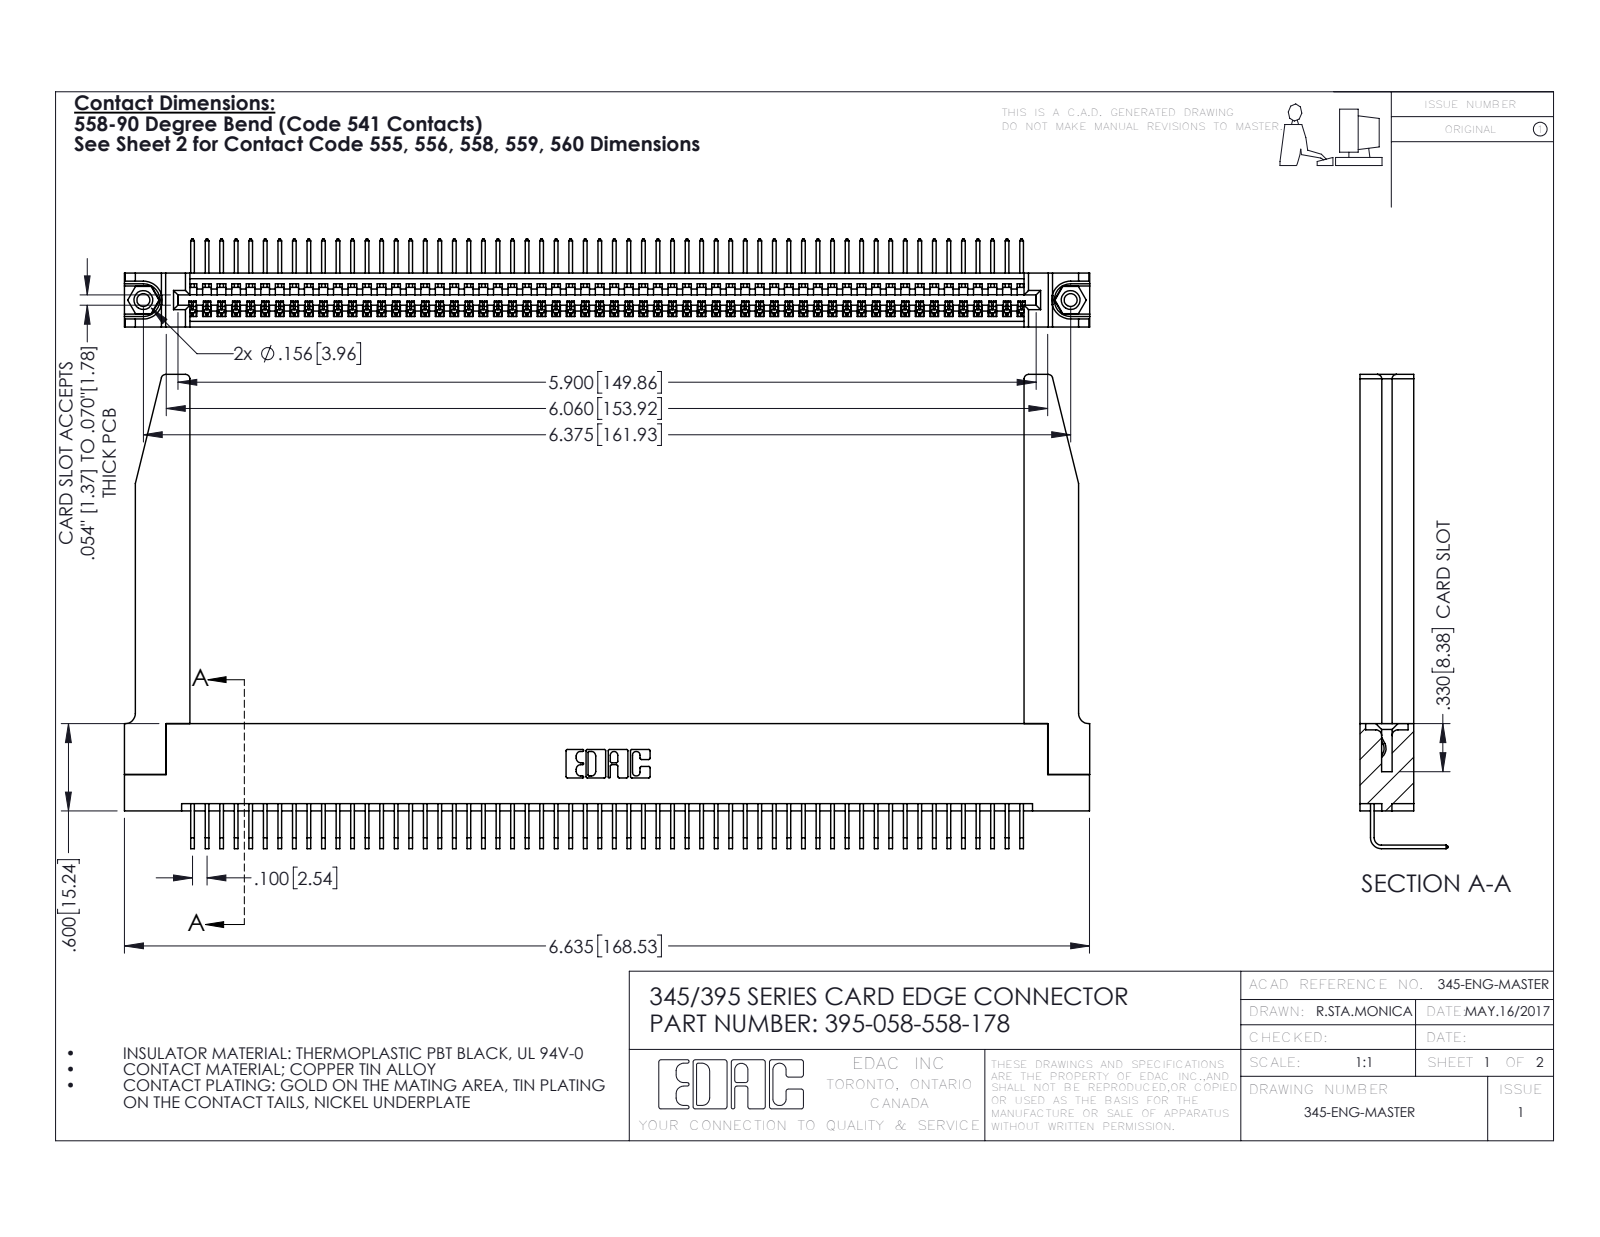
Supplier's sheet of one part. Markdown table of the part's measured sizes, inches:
| quantity | value |
| --- | --- |
| part name | 395-058-558-178; 345-220-078_345-220-078; 345-250-001_345-250-001-102; 345-292-001_558 Tail - 2 (+1 more) |
| STEP written by | SolidWorks 2016 (CONFIG_CONTROL_DESIGN) |
| units | inches |
| bodies | 63 solids, 3840 faces (2658 planar, 1130 cylindrical, 52 other) |
| overall size | 6.636 × 3.259 × 0.605 |
| volume | 1.471 in³ |
| surface area | 46.35 in² |
| round holes (diameter × count) | 0.089 × 2, 0.125 × 2, 0.156 × 2, 0.064 × 1 |
| round bosses / shafts (diameter × count) | 0.155 × 2 |
| partial cylindrical surfaces (radius × count) | 0.006 × 116, 0.01 × 22, 0.03 × 8, 0.007 × 6, 0.031 × 6, 0.026 × 3, 0.031 × 2, 0.04 × 2 |
| main face-to-face distances | 0.072, 0.37, 0.298, 0.2, 0.098, 0.272, 0.025, 0.225, 0.15, 0.148 |
| hole center spacings | 0.27, 6.139, 6.375 |
